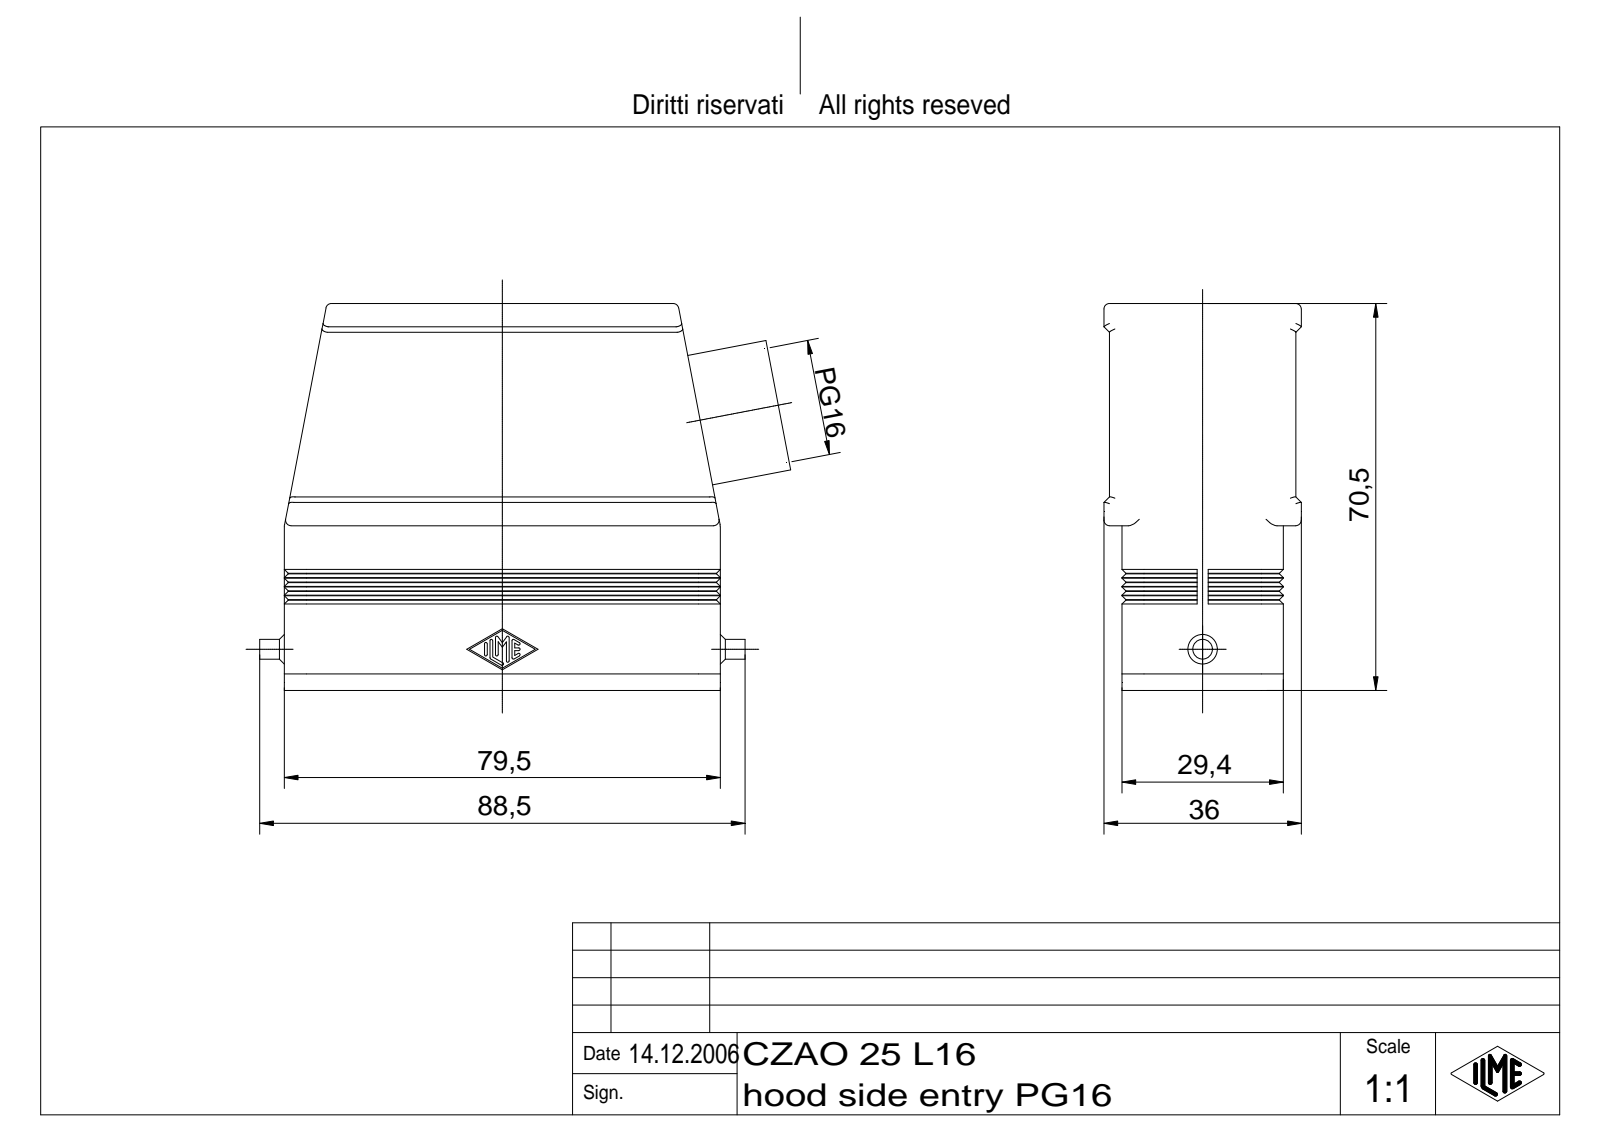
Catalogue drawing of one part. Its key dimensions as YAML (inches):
part_name: "CZ_MZ Tüllengehäuse 1 Bügel"
step_written_by: "Autodesk Inventor 7 (AUTOMOTIVE_DESIGN)"
units: inches
bodies: {solids: 1, faces: 411, planar: 169, cylindrical: 146, other: 96}
overall_size: [3.811, 2.776, 1.417]
volume: 4.032
surface_area: 56.35
round_holes:
  - {diameter: 0.097, count: 4}
  - {diameter: 0.138, count: 4}
  - {diameter: 0.754, count: 1}
  - {diameter: 0.833, count: 1}
  - {diameter: 0.945, count: 1}
round_bosses_or_shafts:
  - {diameter: 0.945, count: 1}
  - {diameter: 0.906, count: 1}
  - {diameter: 0.142, count: 1}
partial_cylinders:
  - {radius: 0.039, count: 24}
  - {radius: 0.01, count: 14}
  - {radius: 0.157, count: 8}
  - {radius: 0.079, count: 6}
  - {radius: 0.049, count: 4}
  - {radius: 0.13, count: 2}
face_to_face_distances: [0.118, 0.921, 1.039, 1.13, 0.209, 0.091, 1.248, 1.157, 0.13, 0.248]
hole_center_spacings: [0.63, 2.598, 2.674]
